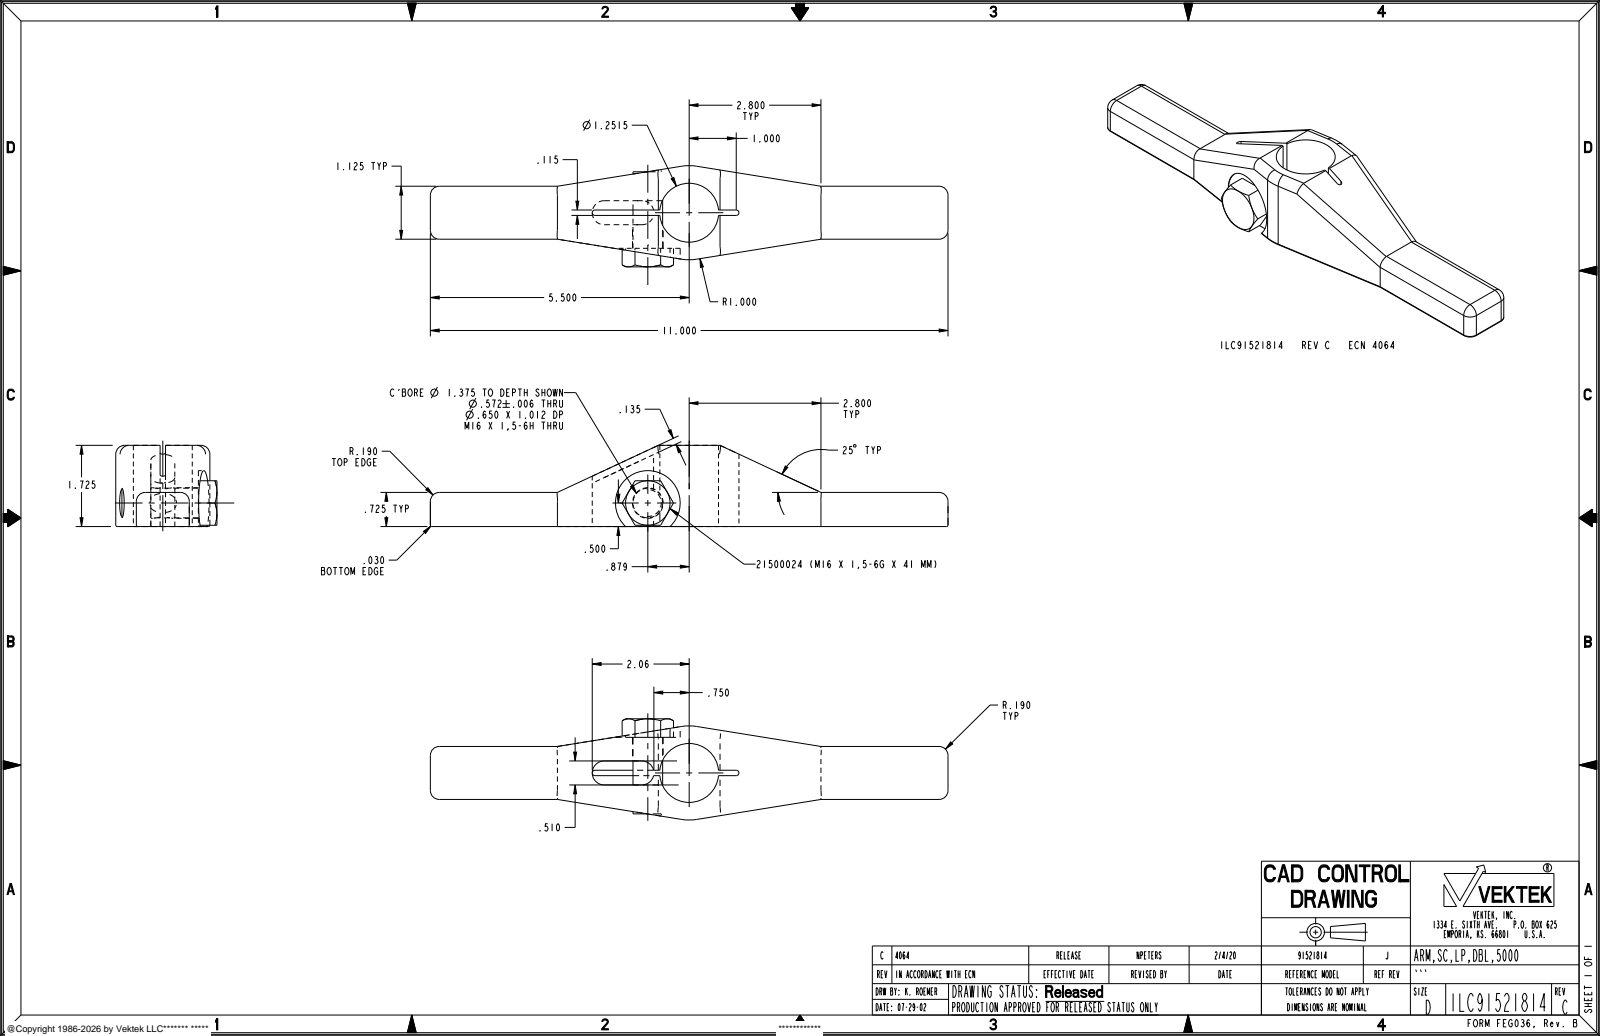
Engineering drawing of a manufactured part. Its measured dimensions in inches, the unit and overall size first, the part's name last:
Units: inches
Overall size (bounding box): 11 × 2.15 × 1.75
Round holes (diameter × count): ⌀0.65 ×1, ⌀1.251 ×1
Round bosses / shafts (diameter × count): ⌀0.63 ×1
Partial cylindrical surfaces — rounded edges, fillets, slot ends (radius × count): R0.19 ×16, R0.03 ×8, R0.057 ×2, R0.255 ×2, R0.286 ×1, R0.687 ×1, R1 ×1
Main face-to-face distances: 0.75, 1.999, 1.125, 0.505, 0.62, 0.307, 0.818, 0.198, 0.313, 2.001
Volume: 14.08 in³ · Surface area: 66.99 in²
Bodies: 1 solid, 104 faces (37 planar, 49 cylindrical, 18 other)
Part name (STEP PRODUCT): ILC91521814
STEP written by: PRO/ENGINEER BY PARAMETRIC TECHNOLOGY CORPORATION, 2004290 (AUTOMOTIVE_DESIGN_CC2)
